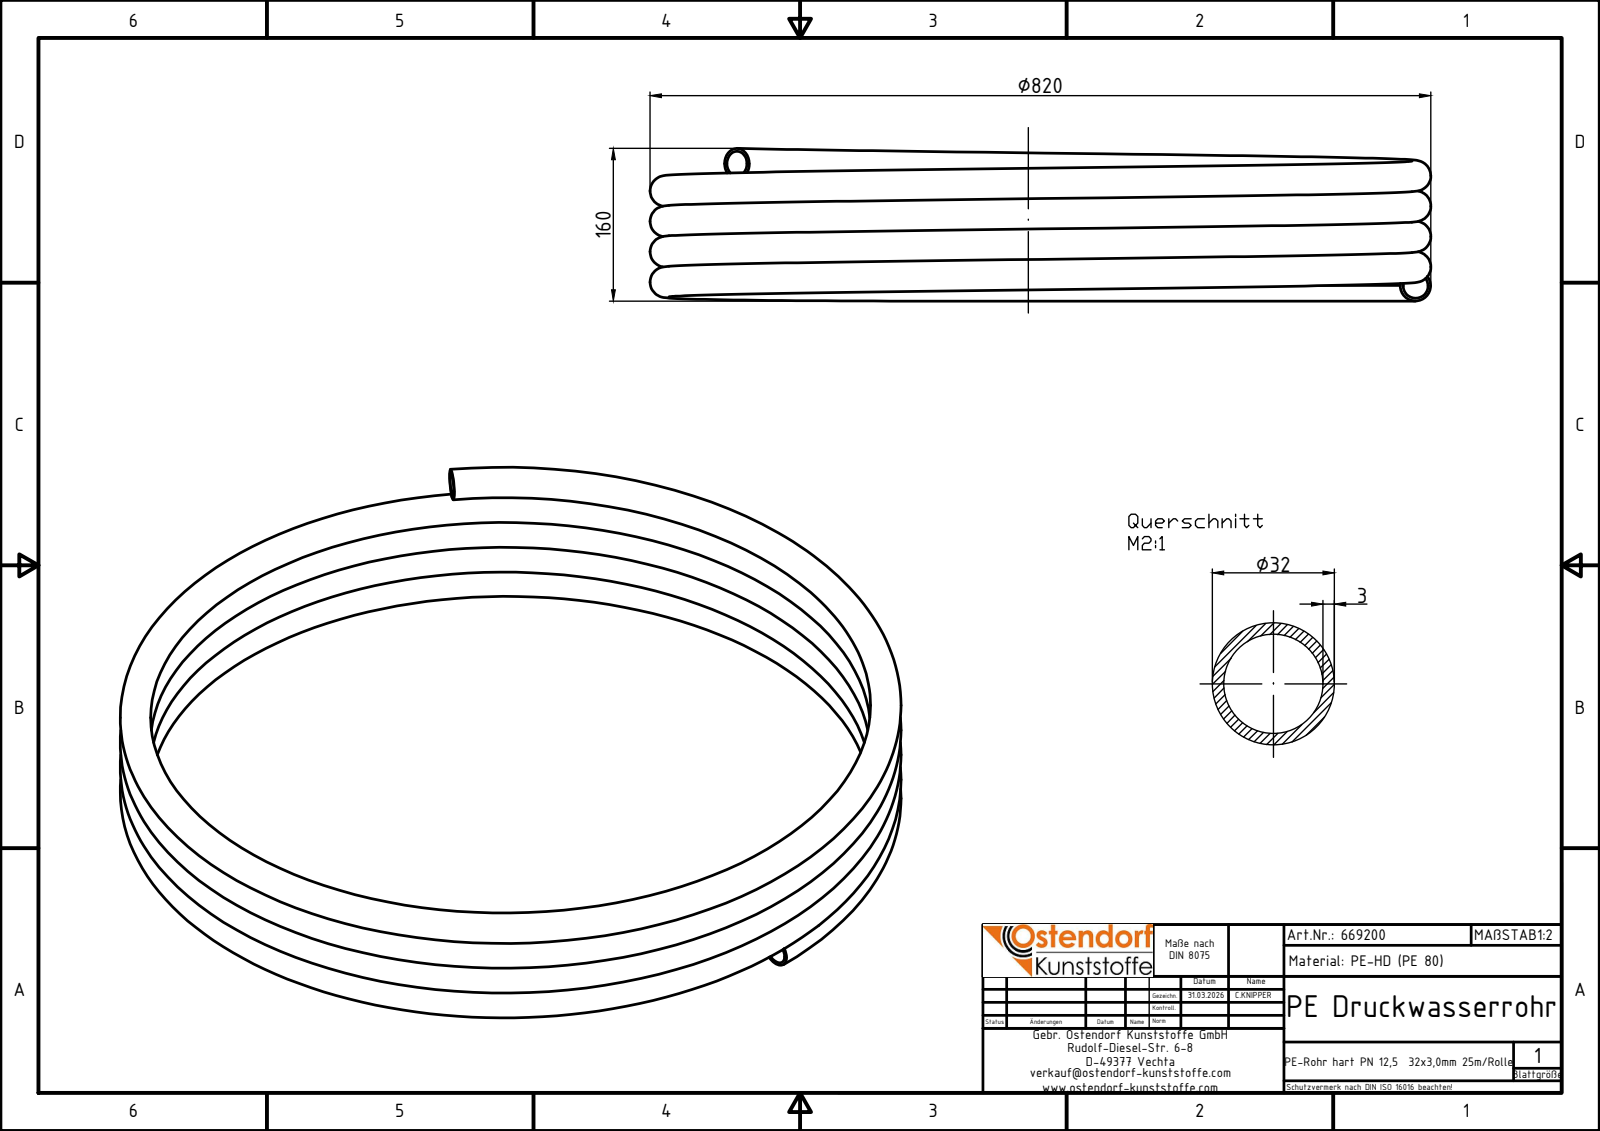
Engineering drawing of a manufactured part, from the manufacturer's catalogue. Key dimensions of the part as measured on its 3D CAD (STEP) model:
Part name (STEP PRODUCT): 669200z
STEP written by: Autodesk Inventor 2024 (AUTOMOTIVE_DESIGN)
Units: millimetres
Bodies: 1 solid, 7 faces (3 planar, 0 cylindrical, 4 other)
Overall size (bounding box): 820.01 × 820.01 × 160.4
Volume: 2 890 000 mm³ · Surface area: 1 899 000 mm²
